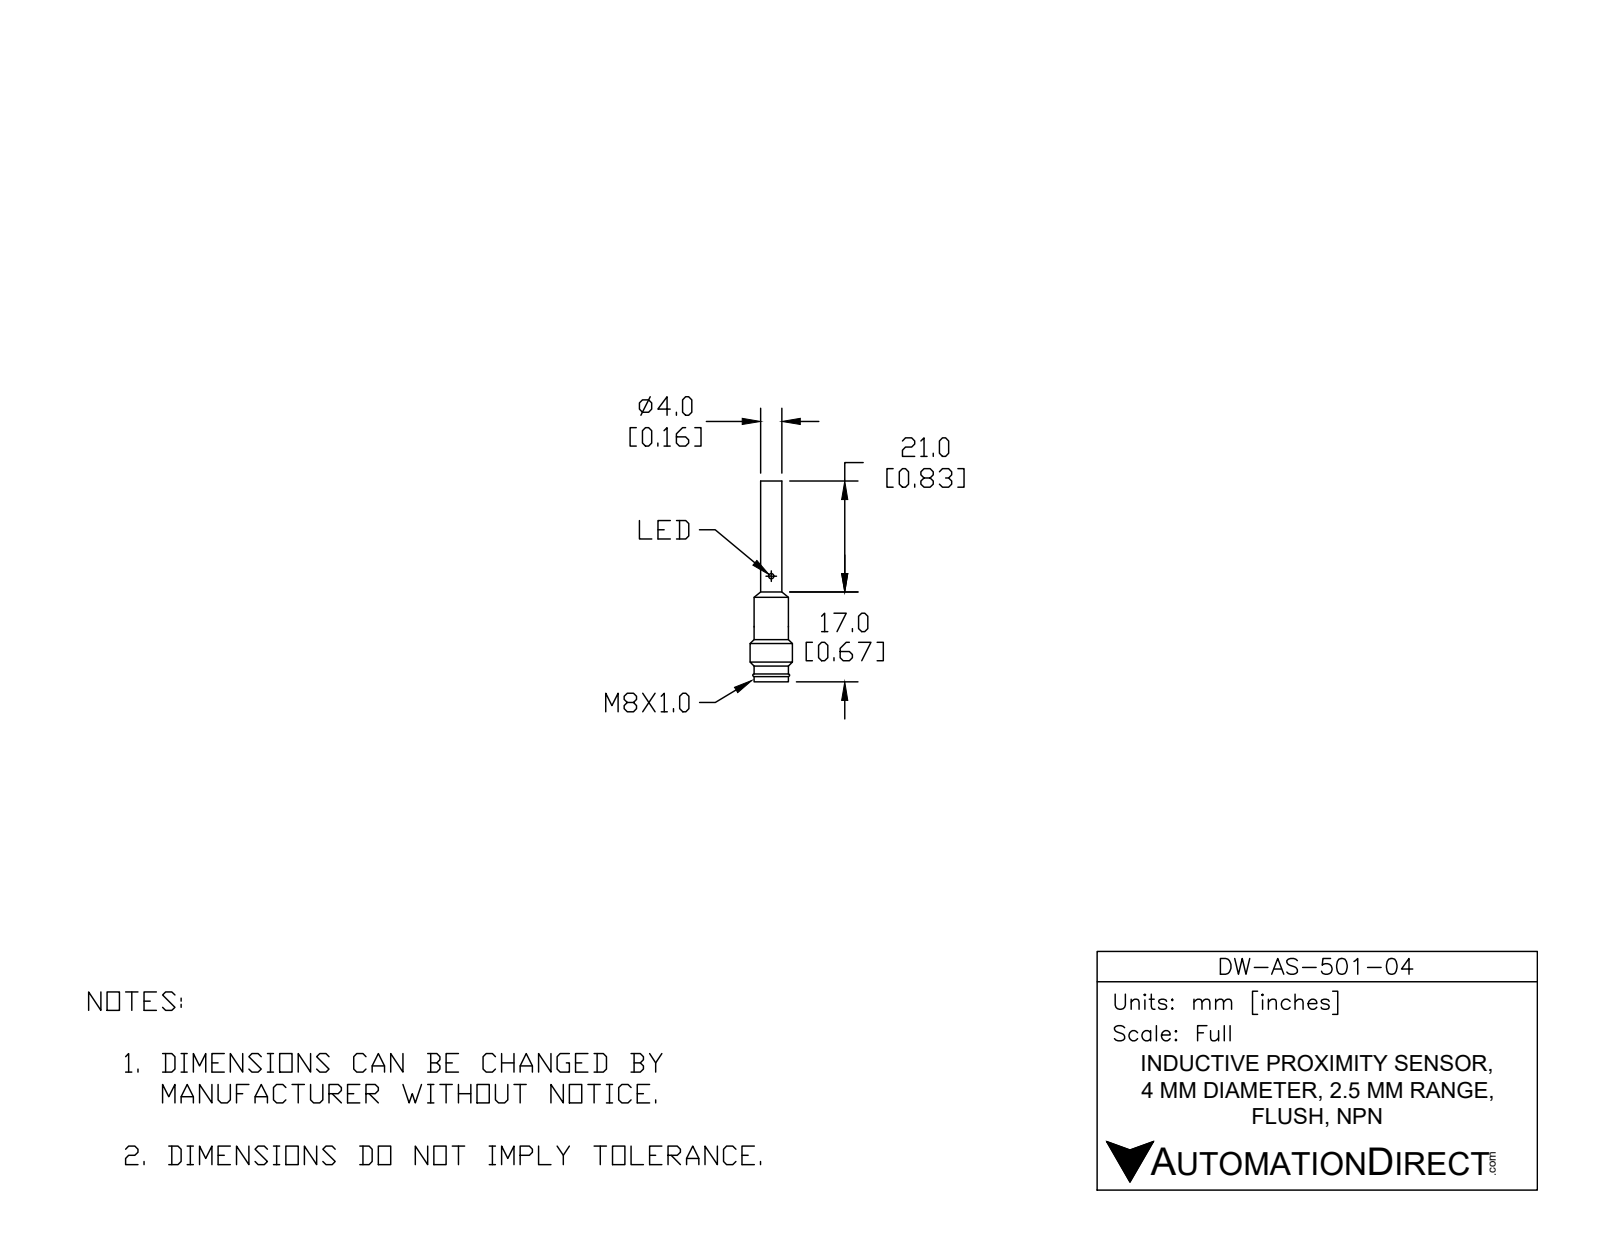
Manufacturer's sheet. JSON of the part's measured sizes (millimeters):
{"part_name": "DW-AS-501-04", "step_written_by": "SolidWorks 2017 (AUTOMOTIVE_DESIGN)", "units": "millimeters", "bodies": {"solids": 3, "faces": 36, "planar": 8, "cylindrical": 13, "other": 15}, "overall_size": [38, 8, 8], "volume_mm3": 460, "surface_area_mm2": 1348, "round_holes": [[1.5, 1], [3.6, 1], [5.8, 1]], "round_bosses_or_shafts": [[1, 3], [8, 1], [6.9, 1], [6.5, 1], [5.6, 1], [4, 1], [3.4, 1]], "face_to_face_distances": [8.5, 24.5, 33, 24.5, 32.9, 1.3, 1.2, 23.2, 31.7, 1.2]}
